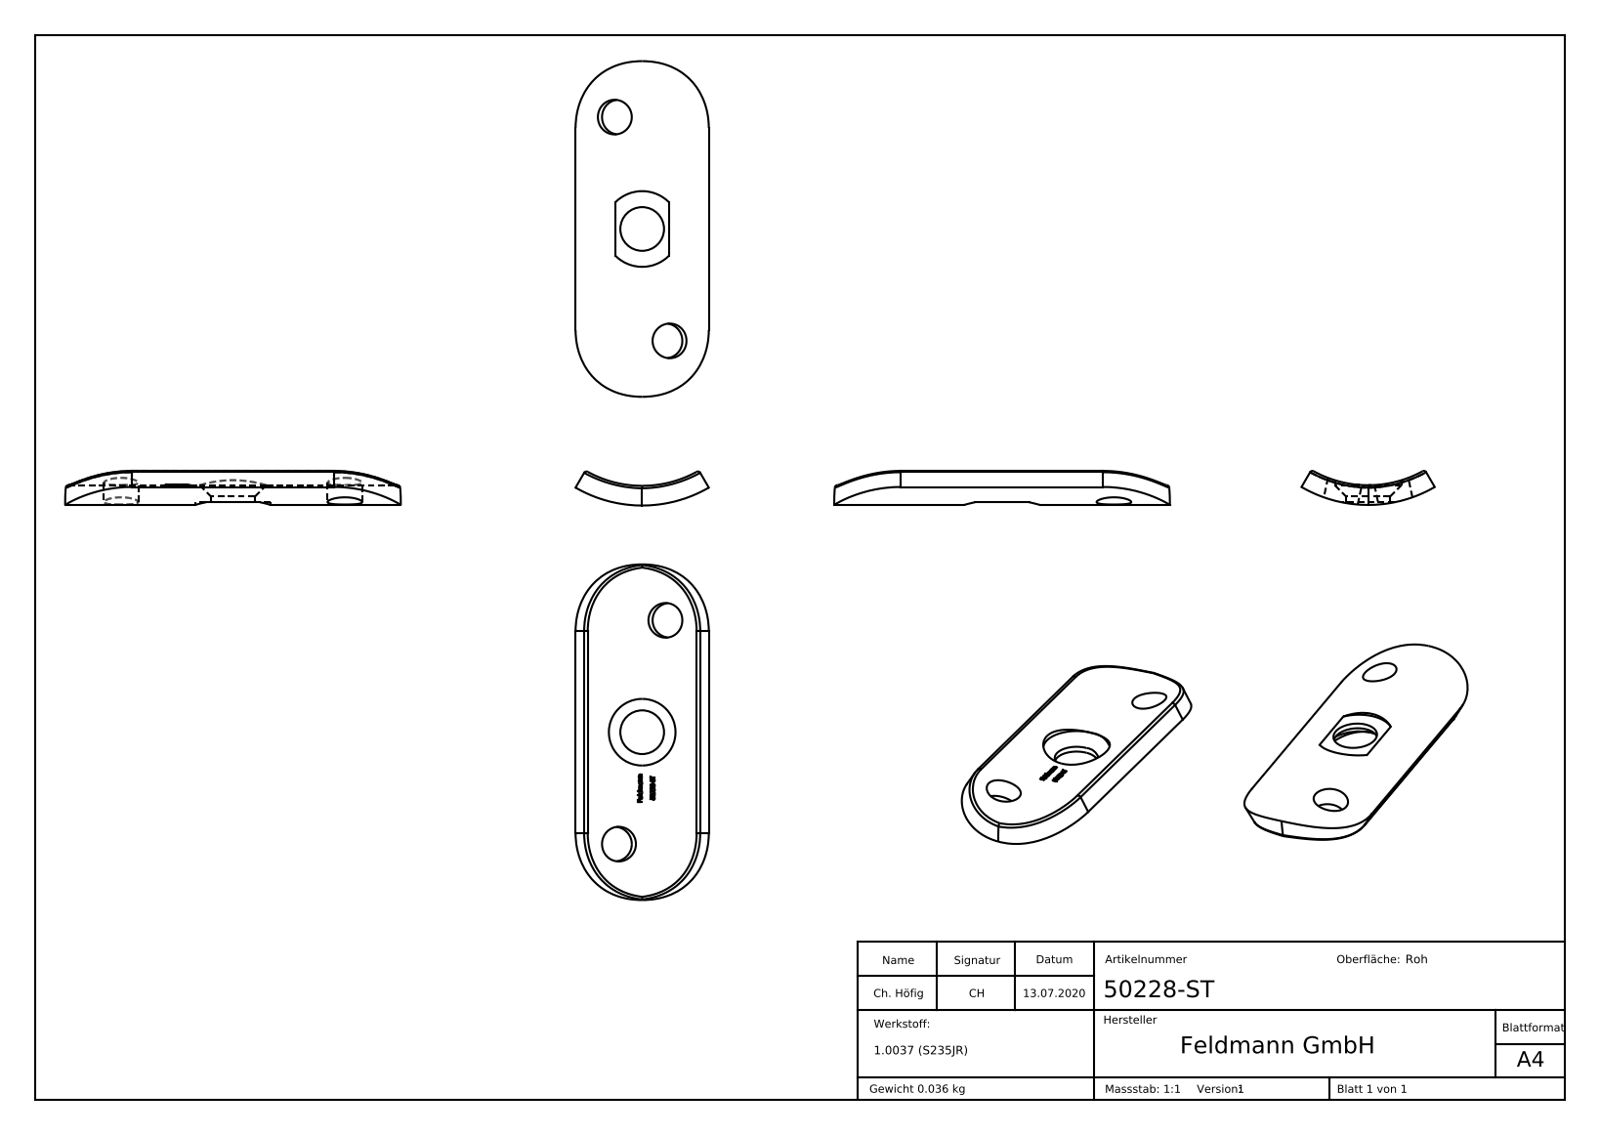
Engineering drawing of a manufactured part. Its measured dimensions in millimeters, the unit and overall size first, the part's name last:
Units: millimetres
Overall size (bounding box): 63 × 25 × 6.39
Round holes (diameter × count): ⌀6.5 ×2, ⌀8.2 ×1, ⌀12.5 ×1
Partial cylindrical surfaces — rounded edges, fillets, slot ends (radius × count): R12.5 ×4, R0.5 ×2, R7.1 ×1, R21.2 ×1, R21.3 ×1, R24.9 ×1
Main face-to-face distances: 1.78, 0.44, 0.79, 2.61, 0.83, 0.71, 2.54, 0.99, 2.27, 0.67
Volume: 4 583 mm³ · Surface area: 3 319 mm²
Bodies: 1 solid, 245 faces (89 planar, 41 cylindrical, 115 other)
Part name (STEP PRODUCT): 50228-ST
STEP written by: SolidWorks 2018 (CONFIG_CONTROL_DESIGN)
